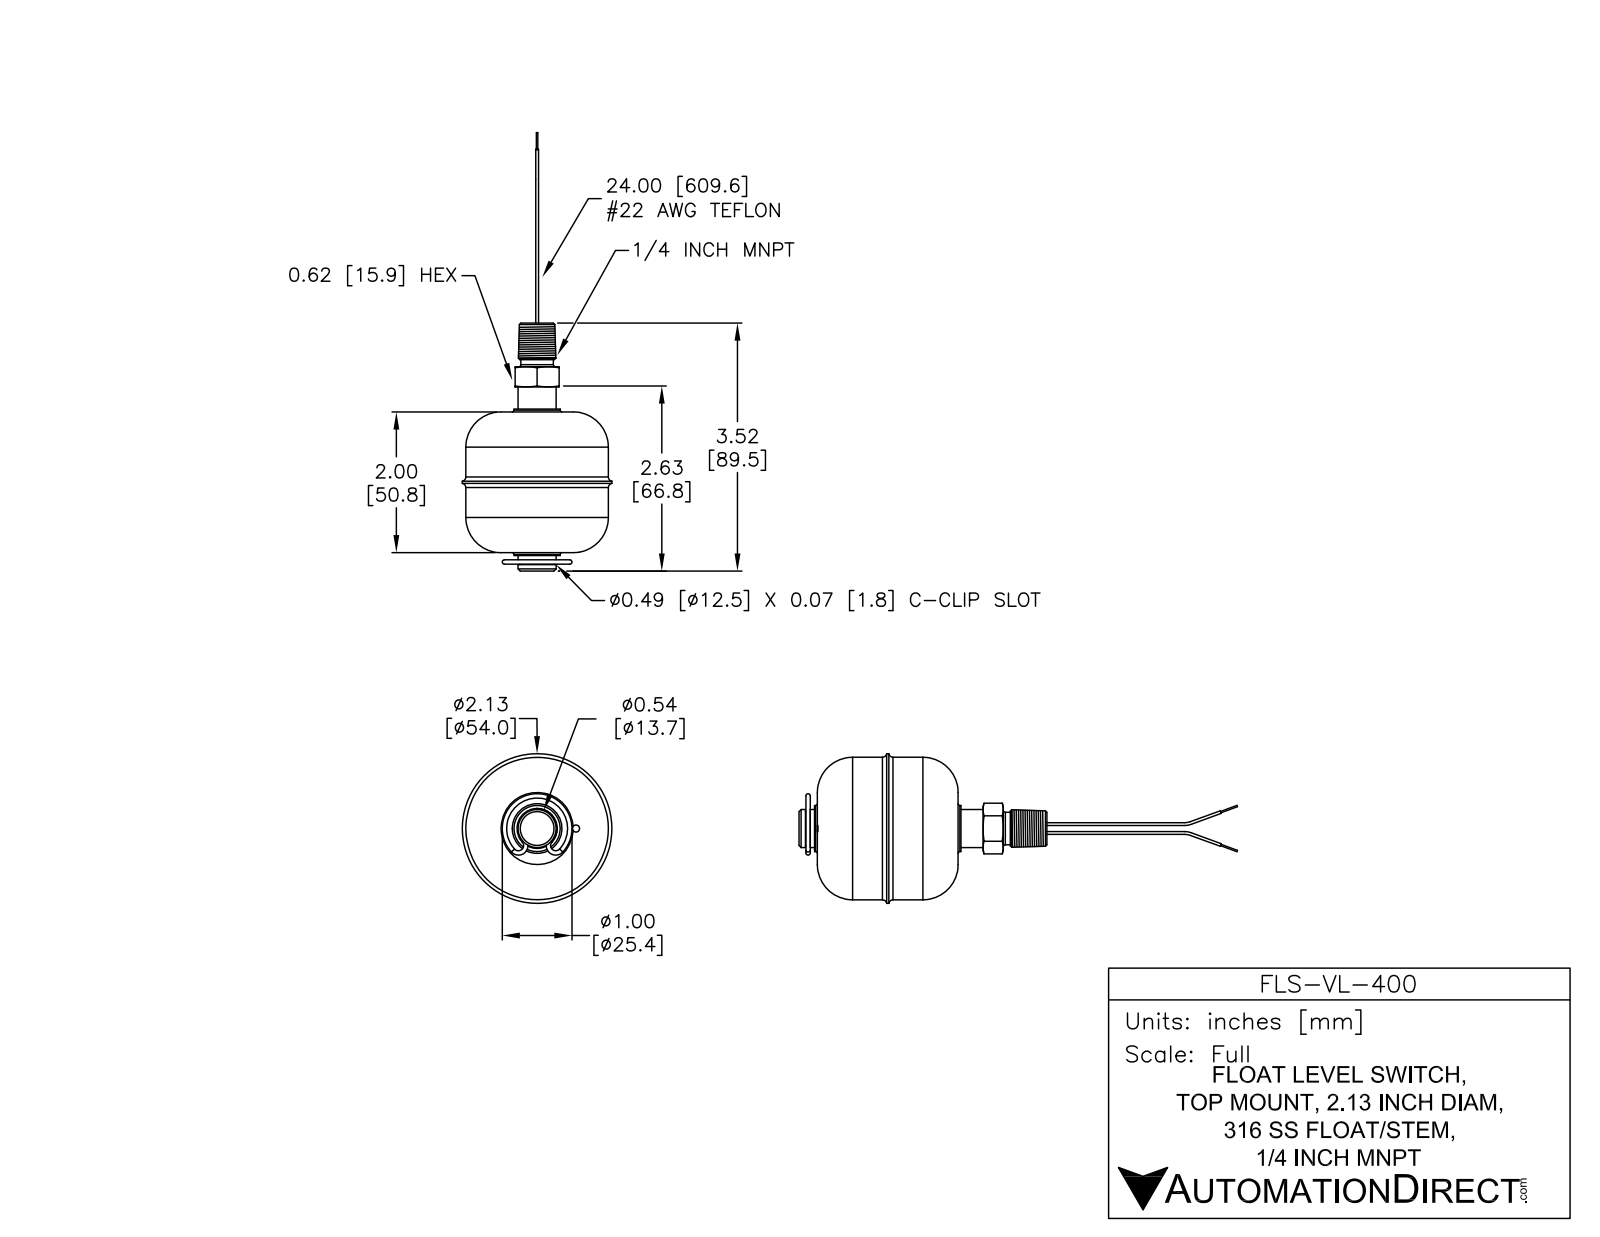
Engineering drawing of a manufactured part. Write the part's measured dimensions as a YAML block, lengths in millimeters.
part_name: "FLS-VL-400"
step_written_by: "SolidWorks 2013 (AUTOMOTIVE_DESIGN)"
units: millimeters
bodies: {solids: 6, faces: 94, planar: 26, cylindrical: 34, other: 34}
overall_size: [158.2, 54, 54]
volume: 94130
surface_area: 20970
round_holes:
  - {diameter: 11.7, count: 1}
  - {diameter: 14.2, count: 1}
round_bosses_or_shafts:
  - {diameter: 1, count: 4}
  - {diameter: 0.5, count: 2}
  - {diameter: 54, count: 1}
  - {diameter: 51.4, count: 1}
  - {diameter: 51.4, count: 1}
  - {diameter: 16.7, count: 1}
  - {diameter: 13.5, count: 1}
  - {diameter: 11.4, count: 1}
face_to_face_distances: [50.8, 4.6, 55.4, 15.9, 70.1, 65.5, 14.7, 1.8, 2.8, 53.6]
